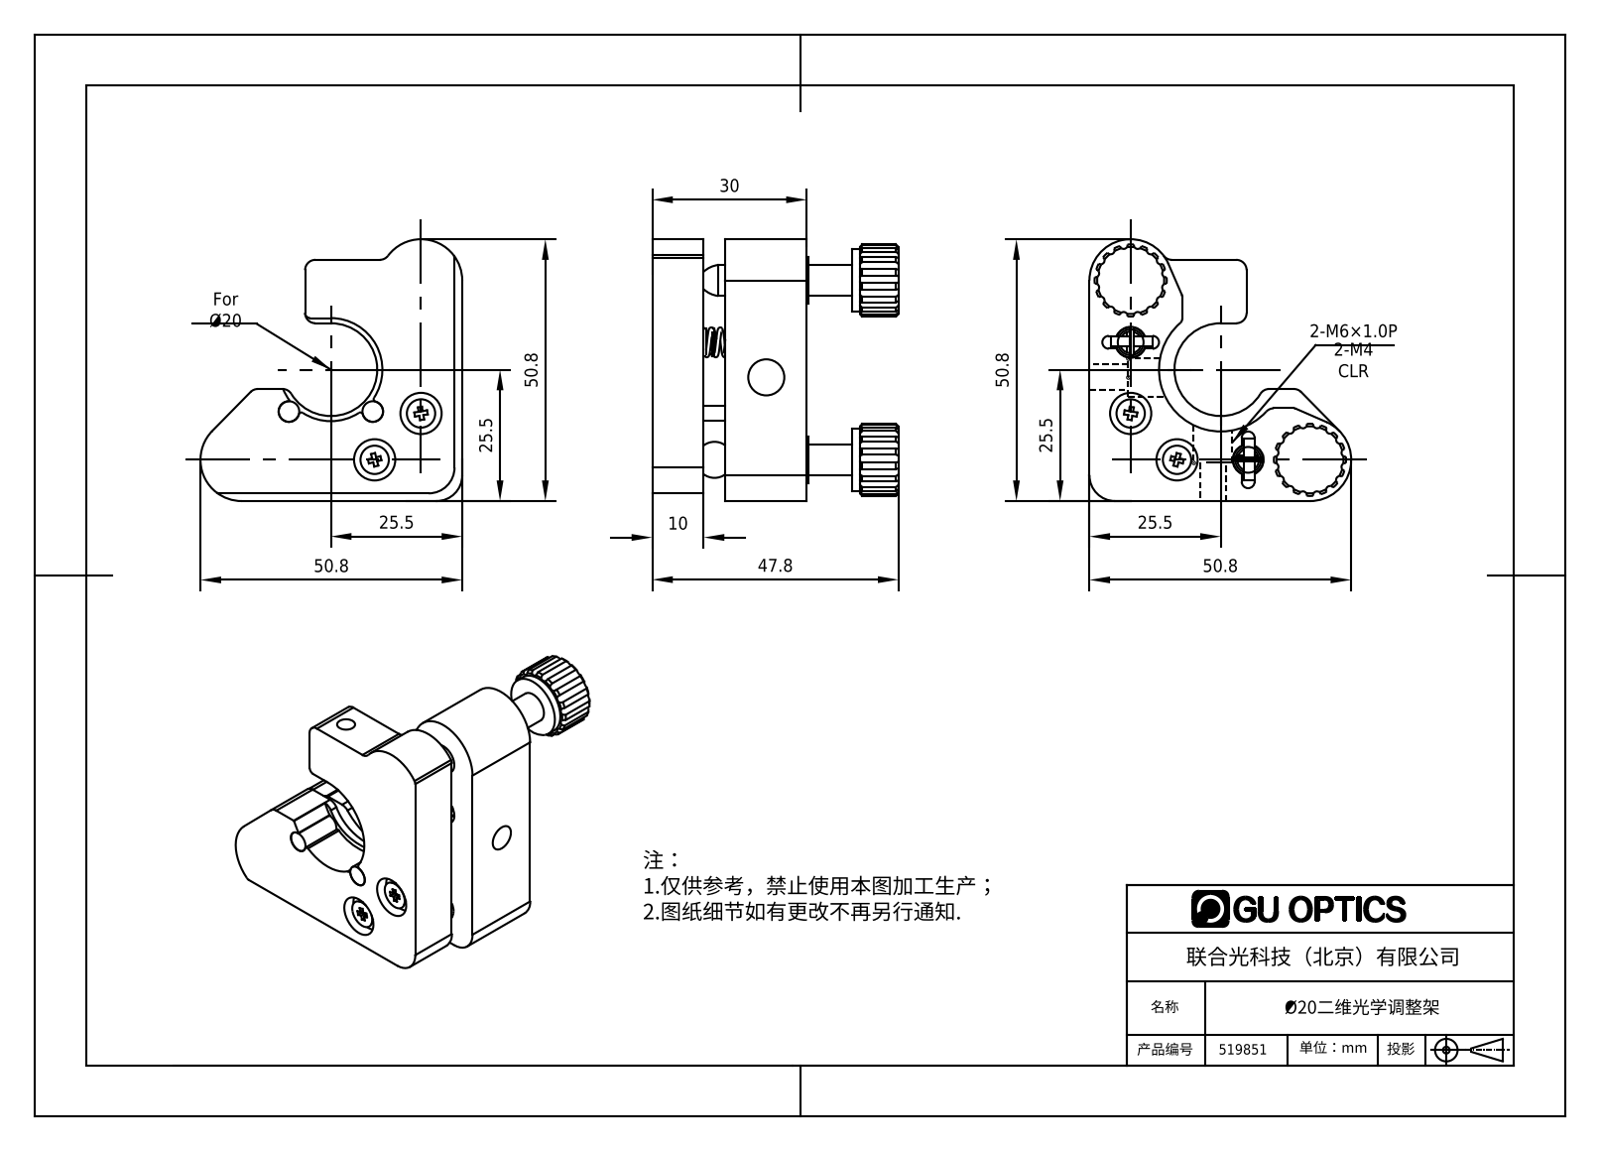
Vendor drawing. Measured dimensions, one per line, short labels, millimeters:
name: 519851
written by: SolidWorks 2016 (AUTOMOTIVE_DESIGN)
unit: mm
bodies: 0 solids, 620 faces (210 planar, 203 cylindrical, 207 other)
size: 50.8 × 50.8 × 47.8
holes: 4× ⌀6, 4× ⌀8, 3× ⌀4, 2× ⌀5, 2× ⌀7.5, 1× ⌀3.5
bosses: 2× ⌀12, 2× ⌀9, 2× ⌀5.4, 2× ⌀3, 2× ⌀2, 2× ⌀0.8, 1× ⌀4
rounds: 32× R0.75, 6× R1, 6× R2, 4× R1.25, 3× R0.5, 2× R5, 2× R7, 2× R8
face distances: 10, 14.2, 4.2, 15.8, 20, 30, 1.5, 37.8, 17.8, 33.6
hole spacings: 12, 13.8, 24.51, 25.8, 35.94, 41.6, 9.37, 9.38
